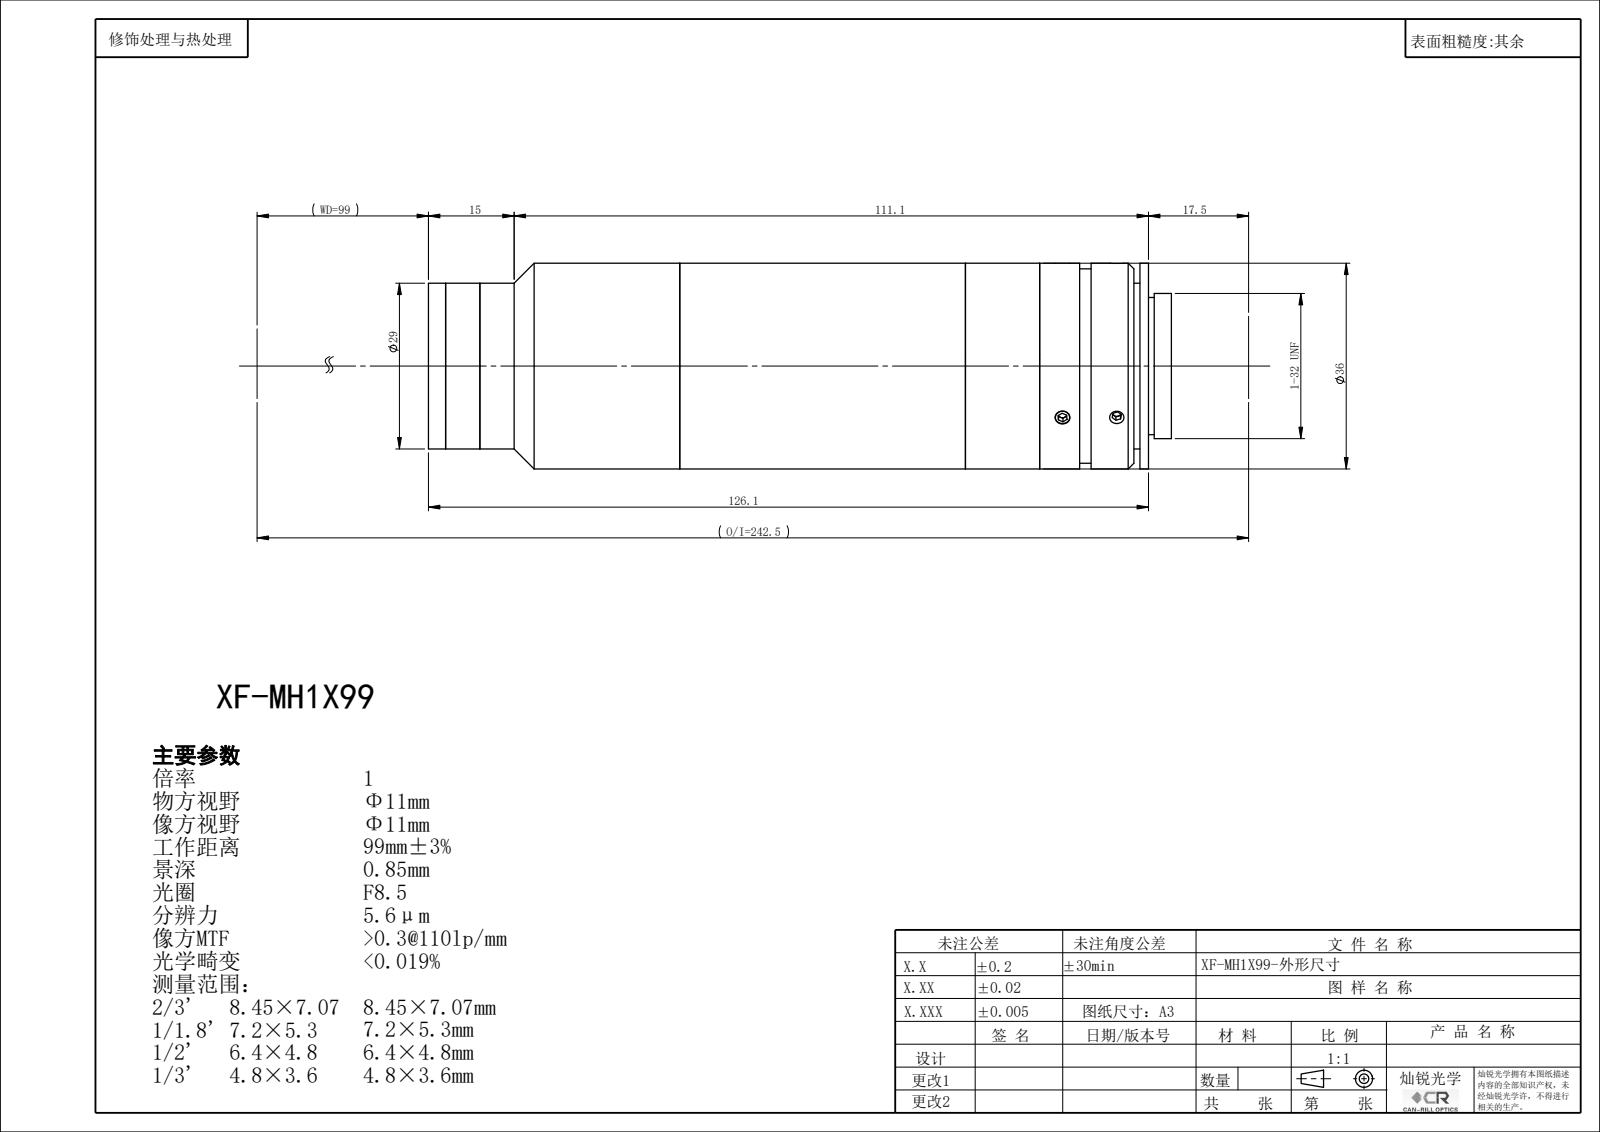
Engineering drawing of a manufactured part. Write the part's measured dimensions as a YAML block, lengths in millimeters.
part_name: "XF-MH1X99"
step_written_by: "SolidWorks 2022 (CONFIG_CONTROL_DESIGN)"
units: millimeters
bodies: {solids: 0, faces: 127, planar: 63, cylindrical: 42, other: 22}
overall_size: [130.05, 36, 36]
round_holes:
  - {diameter: 2.5, count: 3}
  - {diameter: 18, count: 1}
  - {diameter: 22.4, count: 1}
  - {diameter: 24, count: 1}
  - {diameter: 24.9, count: 1}
  - {diameter: 26.4, count: 1}
round_bosses_or_shafts:
  - {diameter: 36, count: 1}
  - {diameter: 34, count: 1}
  - {diameter: 29, count: 1}
  - {diameter: 25.4, count: 1}
face_to_face_distances: [1.5, 30.55, 32.05, 50, 80.55, 82.05, 69, 19, 11.55, 13.05]
